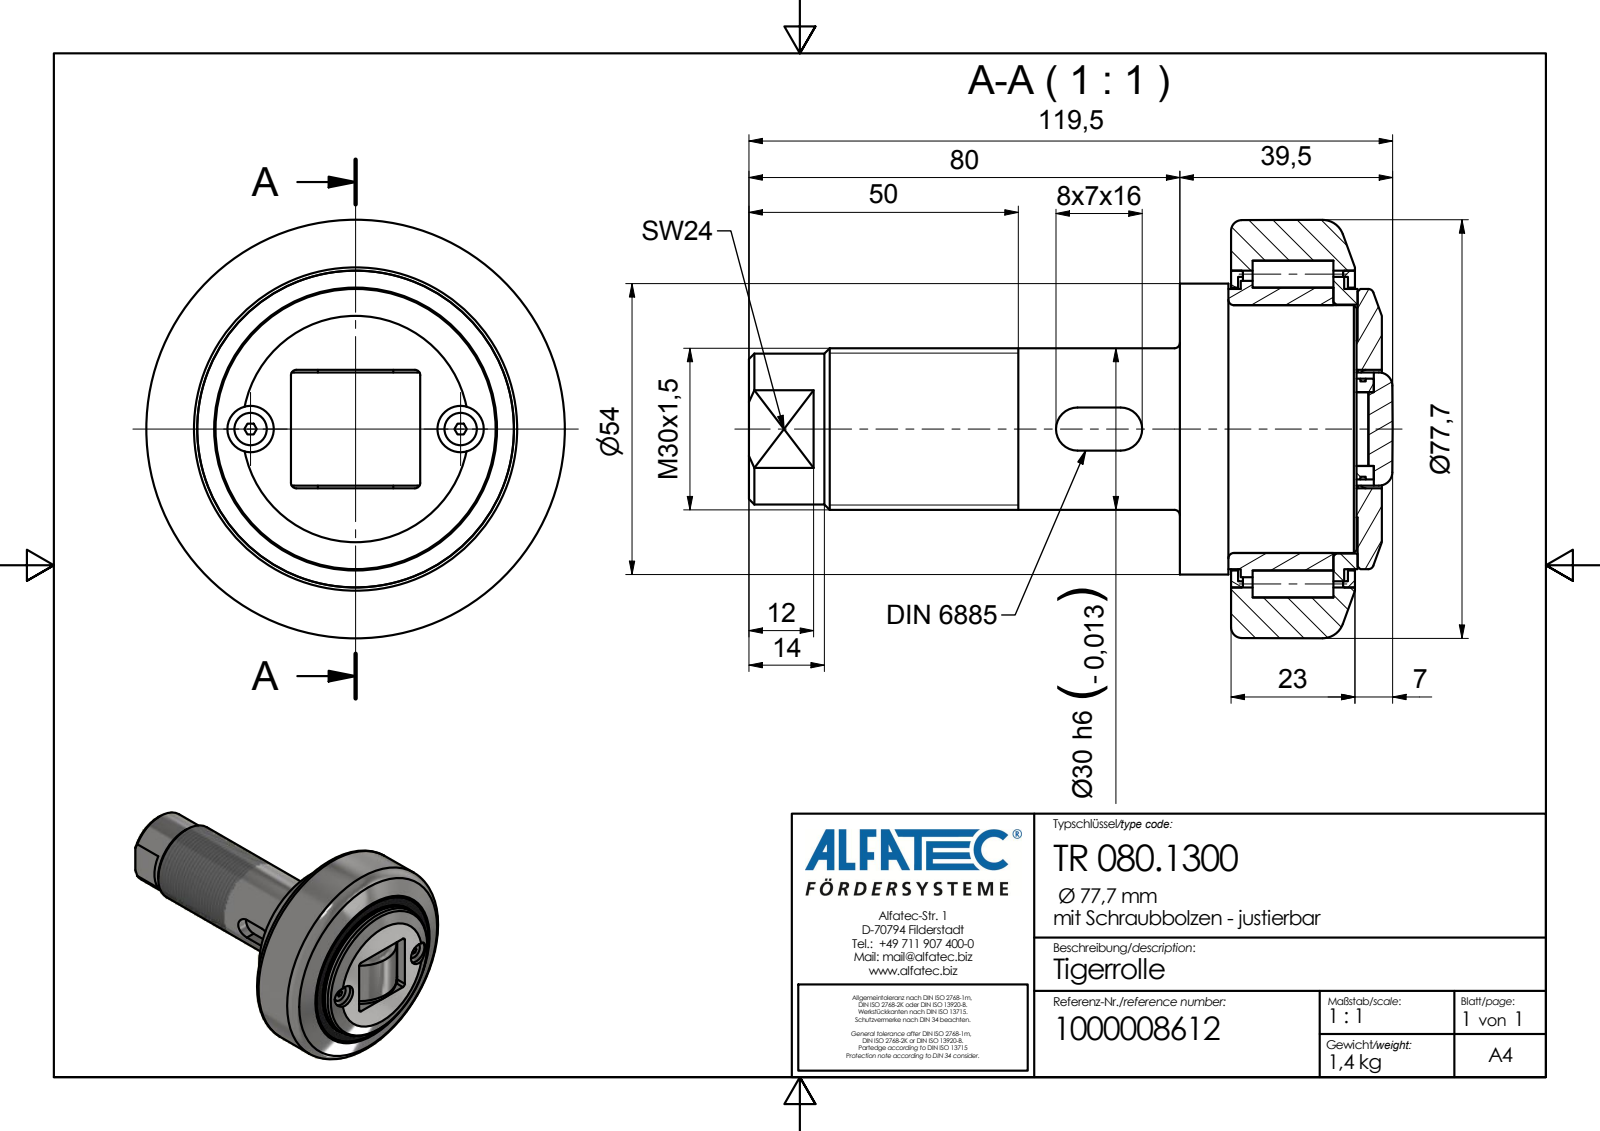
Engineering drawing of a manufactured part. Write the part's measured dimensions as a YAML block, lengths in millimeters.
part_name: "TR 080.1300_Kontur"
step_written_by: "Autodesk Inventor 2020 (AUTOMOTIVE_DESIGN)"
units: millimeters
bodies: {solids: 1, faces: 105, planar: 50, cylindrical: 33, other: 22}
overall_size: [119.5, 77.7, 77.7]
volume: 190259
surface_area: 26919
round_holes:
  - {diameter: 3.24, count: 2}
  - {diameter: 4.5, count: 2}
  - {diameter: 8.6, count: 2}
  - {diameter: 46.2, count: 1}
round_bosses_or_shafts:
  - {diameter: 6, count: 2}
  - {diameter: 3, count: 2}
  - {diameter: 54, count: 1}
  - {diameter: 52, count: 1}
  - {diameter: 32.8, count: 1}
  - {diameter: 30, count: 1}
  - {diameter: 28, count: 1}
partial_cylinders:
  - {radius: 1, count: 4}
  - {radius: 4, count: 2}
  - {radius: 8, count: 1}
  - {radius: 9, count: 1}
  - {radius: 10.5, count: 1}
face_to_face_distances: [9.5, 0.5, 23.5, 32.5, 23, 33, 5, 37.5, 28, 4.5]
hole_center_spacings: [19.5, 39]
